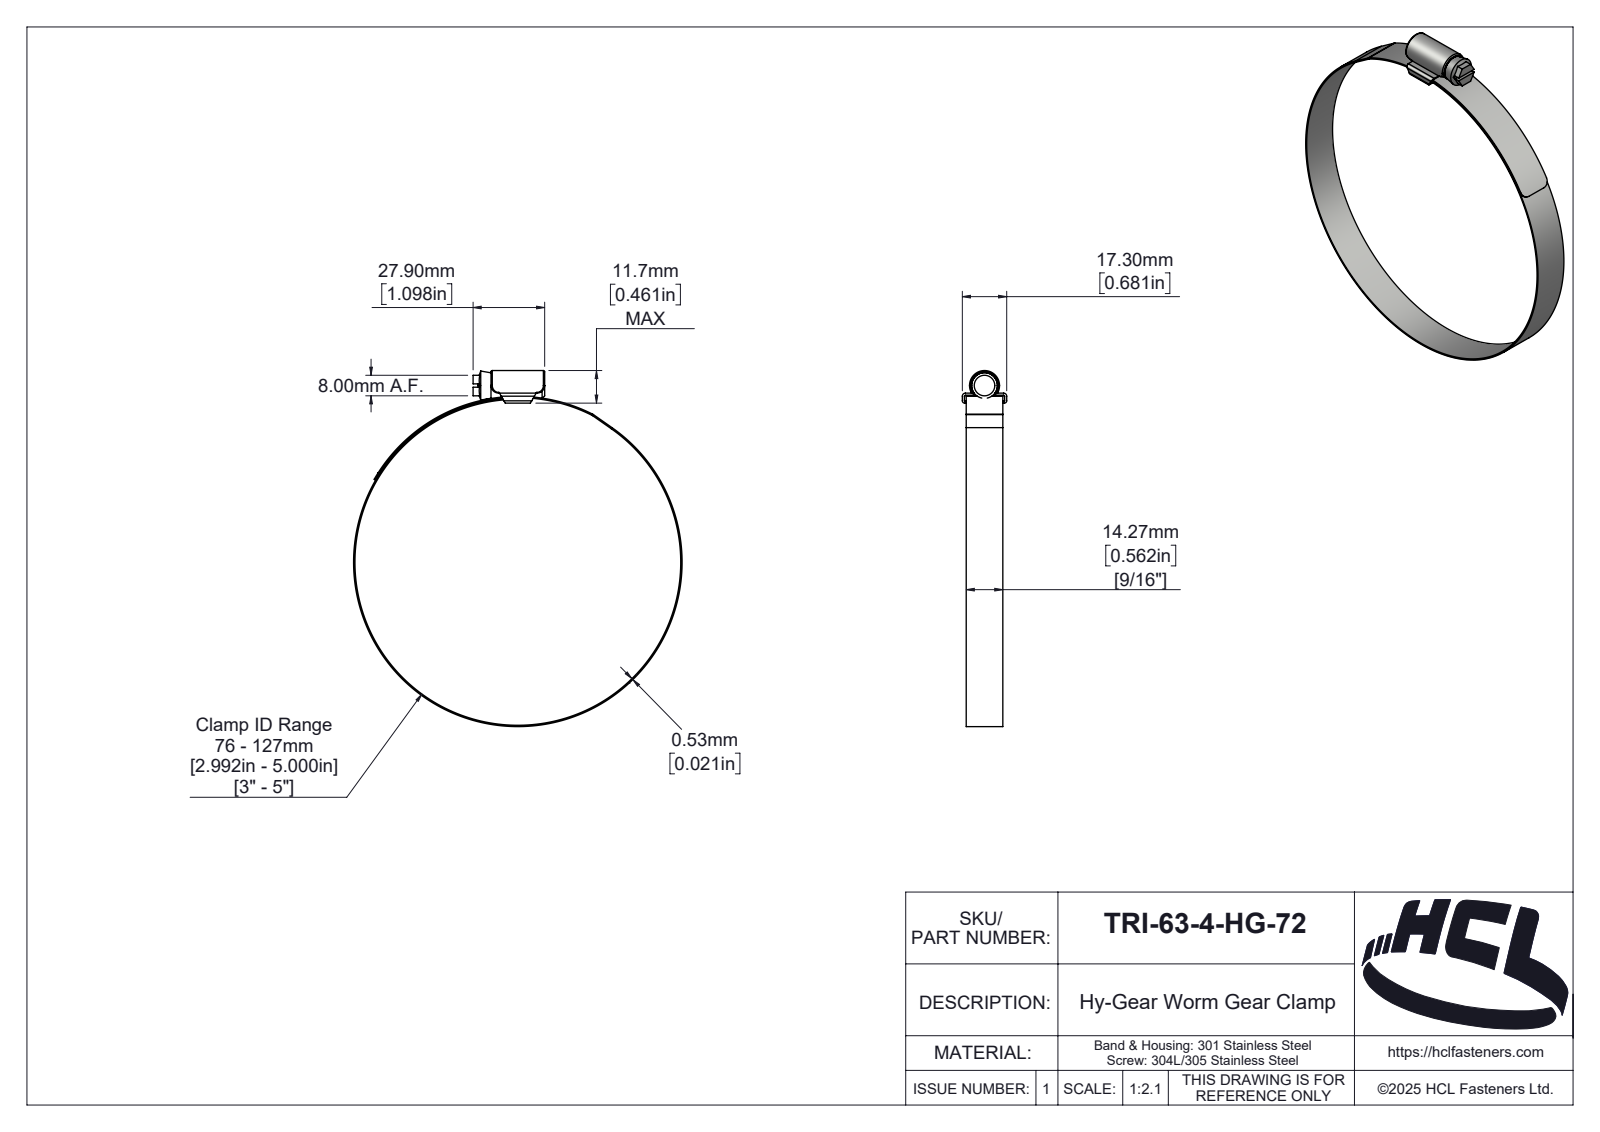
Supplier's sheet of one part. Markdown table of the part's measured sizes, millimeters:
| quantity | value |
| --- | --- |
| part name | TRI-50-0-HG-72 |
| STEP written by | SolidWorks 2025 (AUTOMOTIVE_DESIGN) |
| units | millimeters |
| bodies | 3 solids, 189 faces (39 planar, 89 cylindrical, 61 other) |
| overall size | 138.73 × 128.06 × 17.3 |
| volume | 6 333 mm³ |
| surface area | 16 665 mm² |
| round holes (diameter × count) | 127 × 1 |
| round bosses / shafts (diameter × count) | 128.06 × 1, 10 × 1 |
| partial cylindrical surfaces (radius × count) | 0.5 × 6, 3 × 4, 0.1 × 2, 0.9 × 2, 1.2 × 2, 0.46 × 1, 1.89 × 1, 2 × 1 |
| main face-to-face distances | 0.8, 14.26, 3.1, 0.53, 2.3, 3.9, 27.9, 1.52, 15.78, 16.5 |
